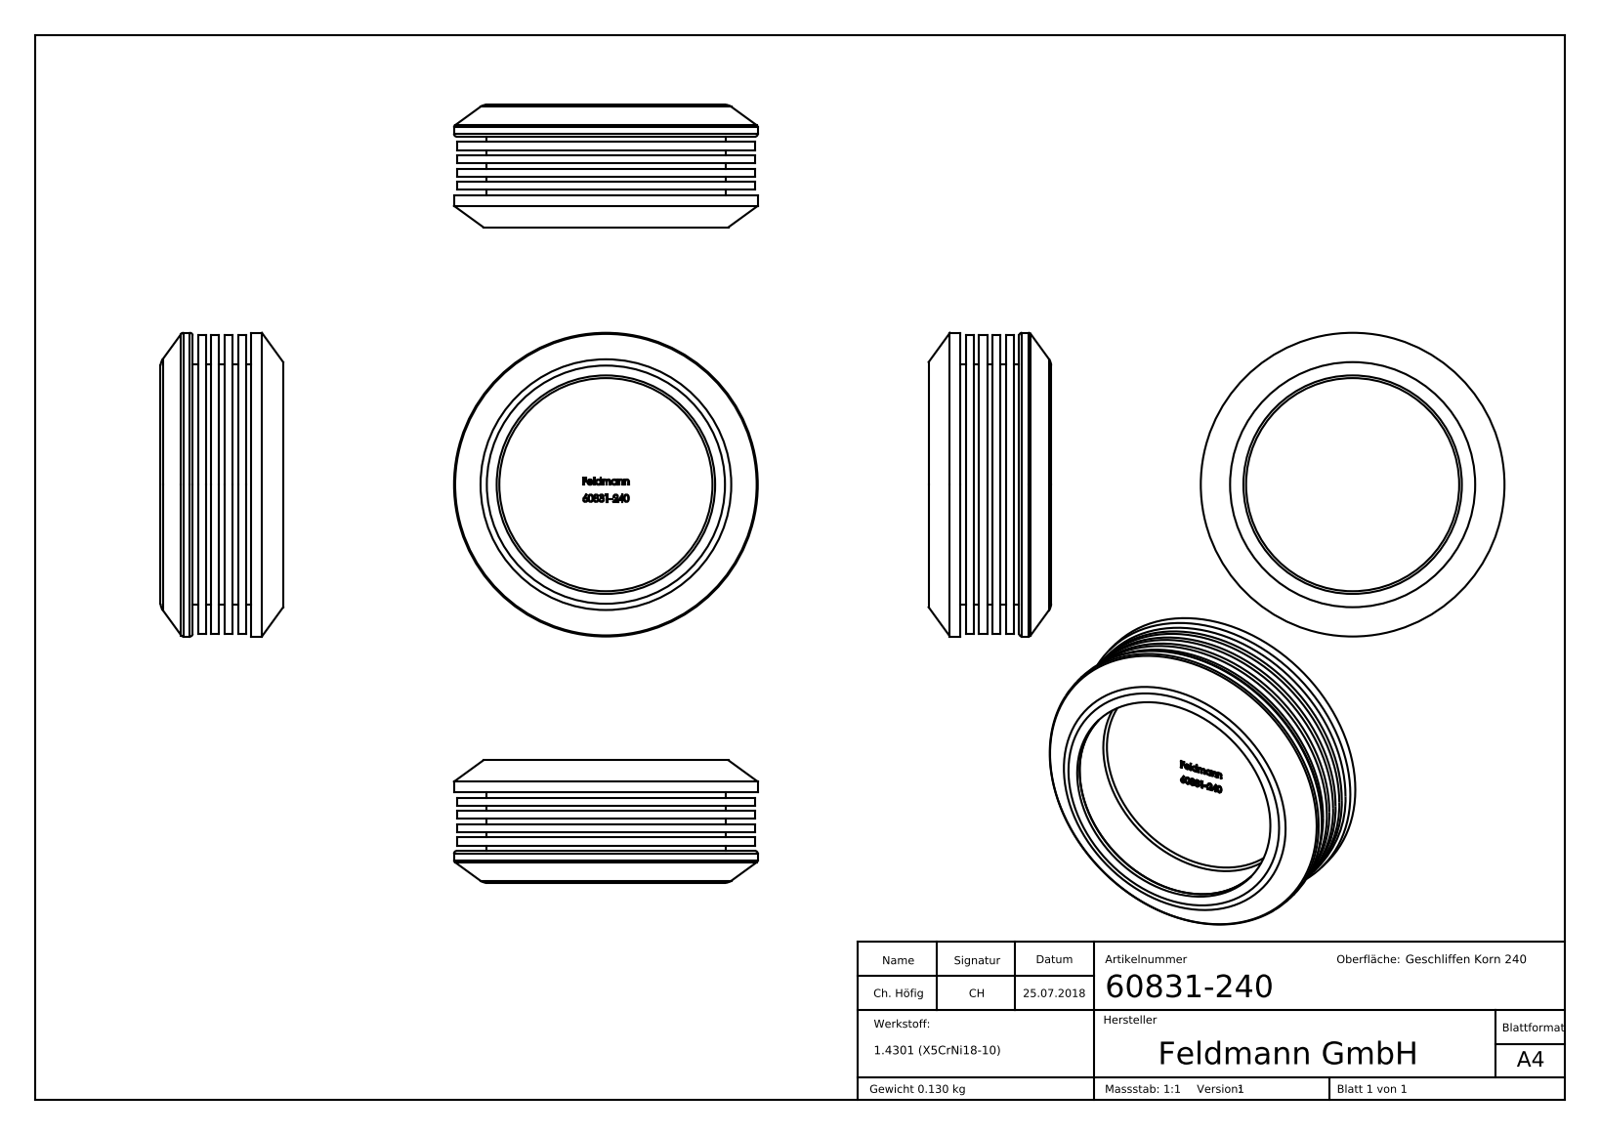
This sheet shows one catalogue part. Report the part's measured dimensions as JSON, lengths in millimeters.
{"part_name": "60831-240 Teil3_60831-240 Teil3; 60831-240; 60831-240 Teil2_60831-240 Teil2; 60831-240 Teil1_60831-240 Teil1", "step_written_by": "SolidWorks 2015 (CONFIG_CONTROL_DESIGN)", "units": "millimeters", "bodies": {"solids": 6, "faces": 293, "planar": 131, "cylindrical": 30, "other": 132}, "overall_size": [57, 57, 23], "volume_mm3": 21002, "surface_area_mm2": 23132, "round_holes": [[41, 1], [43.34, 1], [45.2, 1]], "round_bosses_or_shafts": [[57, 1], [56, 1], [45, 1]], "face_to_face_distances": [2.5, 1, 5, 7.5, 6, 3.5, 1.5, 8.5, 4, 10]}
